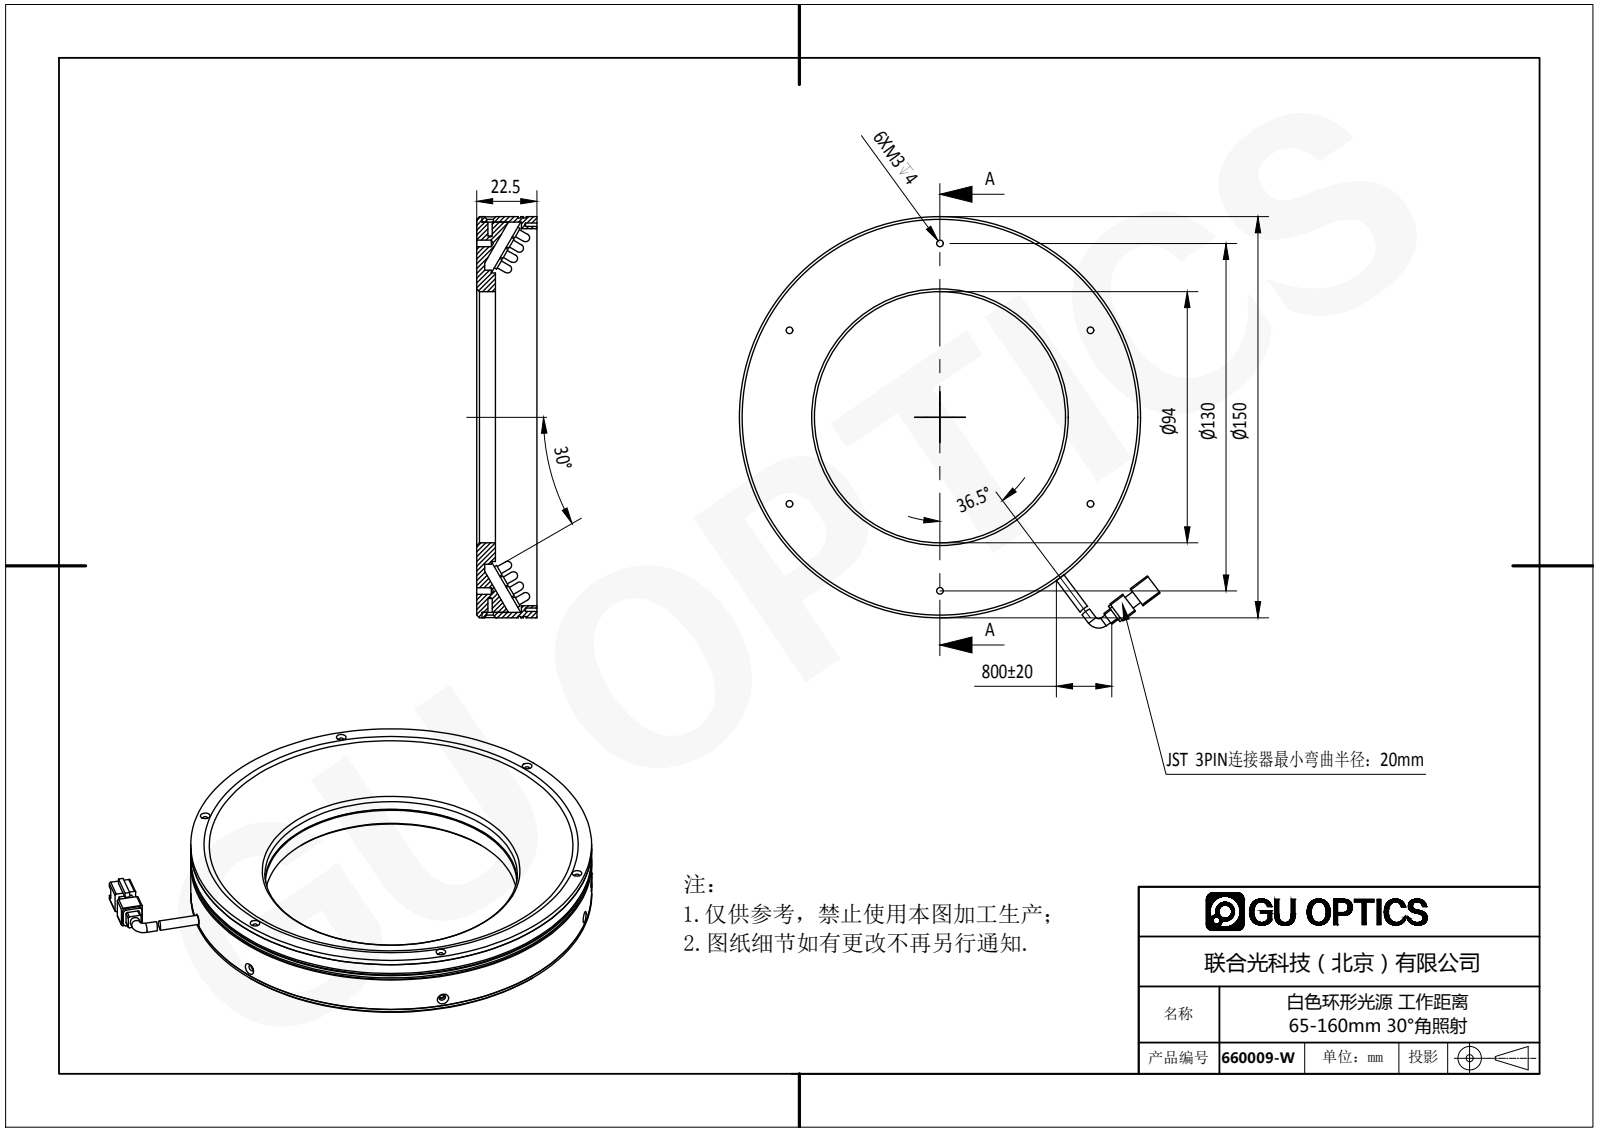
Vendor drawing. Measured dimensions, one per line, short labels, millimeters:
name: 660009-W
written by: SolidWorks 2016 (AUTOMOTIVE_DESIGN)
unit: mm
bodies: 341 solids, 6006 faces (4098 planar, 1478 cylindrical, 430 other)
size: 160.52 × 150 × 24.75
volume: 136 685 mm³; area: 129 773 mm²
holes: 6× ⌀1.25, 6× ⌀1.7, 6× ⌀2.5, 5× ⌀1.6, 5× ⌀2.4, 4× ⌀3.5, 1× ⌀94, 1× ⌀94.4, 1× ⌀141
bosses: 335× ⌀3.8, 335× ⌀3, 2× ⌀3.5, 1× ⌀150, 1× ⌀149, 1× ⌀146, 1× ⌀110, 1× ⌀108
rounds: 8× R0.5, 4× R1, 1× R1.65, 1× R10
face distances: 22.5, 2, 15.5, 7, 1, 17.5, 5, 24.5, 20.5, 3
hole spacings: 65, 68.77, 118.7, 72, 112.58, 124.71, 137, 7
